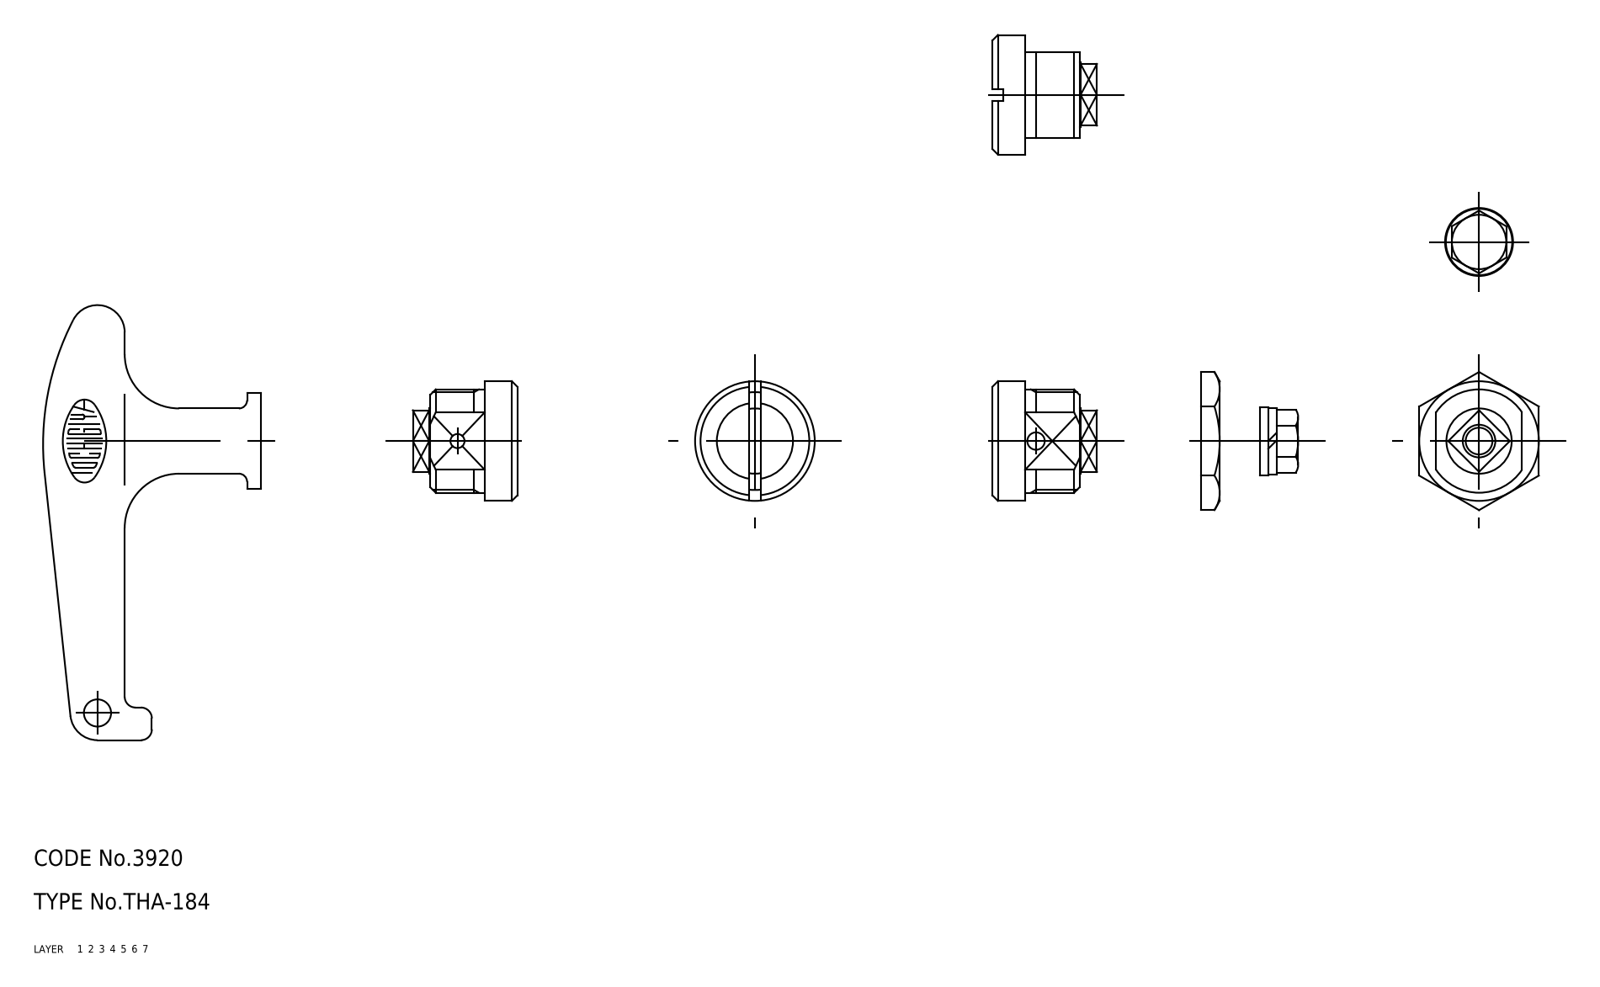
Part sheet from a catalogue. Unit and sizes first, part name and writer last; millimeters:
Units: millimetres
Overall size (bounding box): 84.3 × 80 × 22
Volume: 8 051 mm³ · Surface area: 8 358 mm²
Bodies: 7 solids, 121 faces (0 planar, 0 cylindrical, 121 other)
Part name (STEP PRODUCT): washer_B; washer_A; rotor; nut (+4 more)
STEP written by: CADfix (AUTOMOTIVE_DESIGN)
